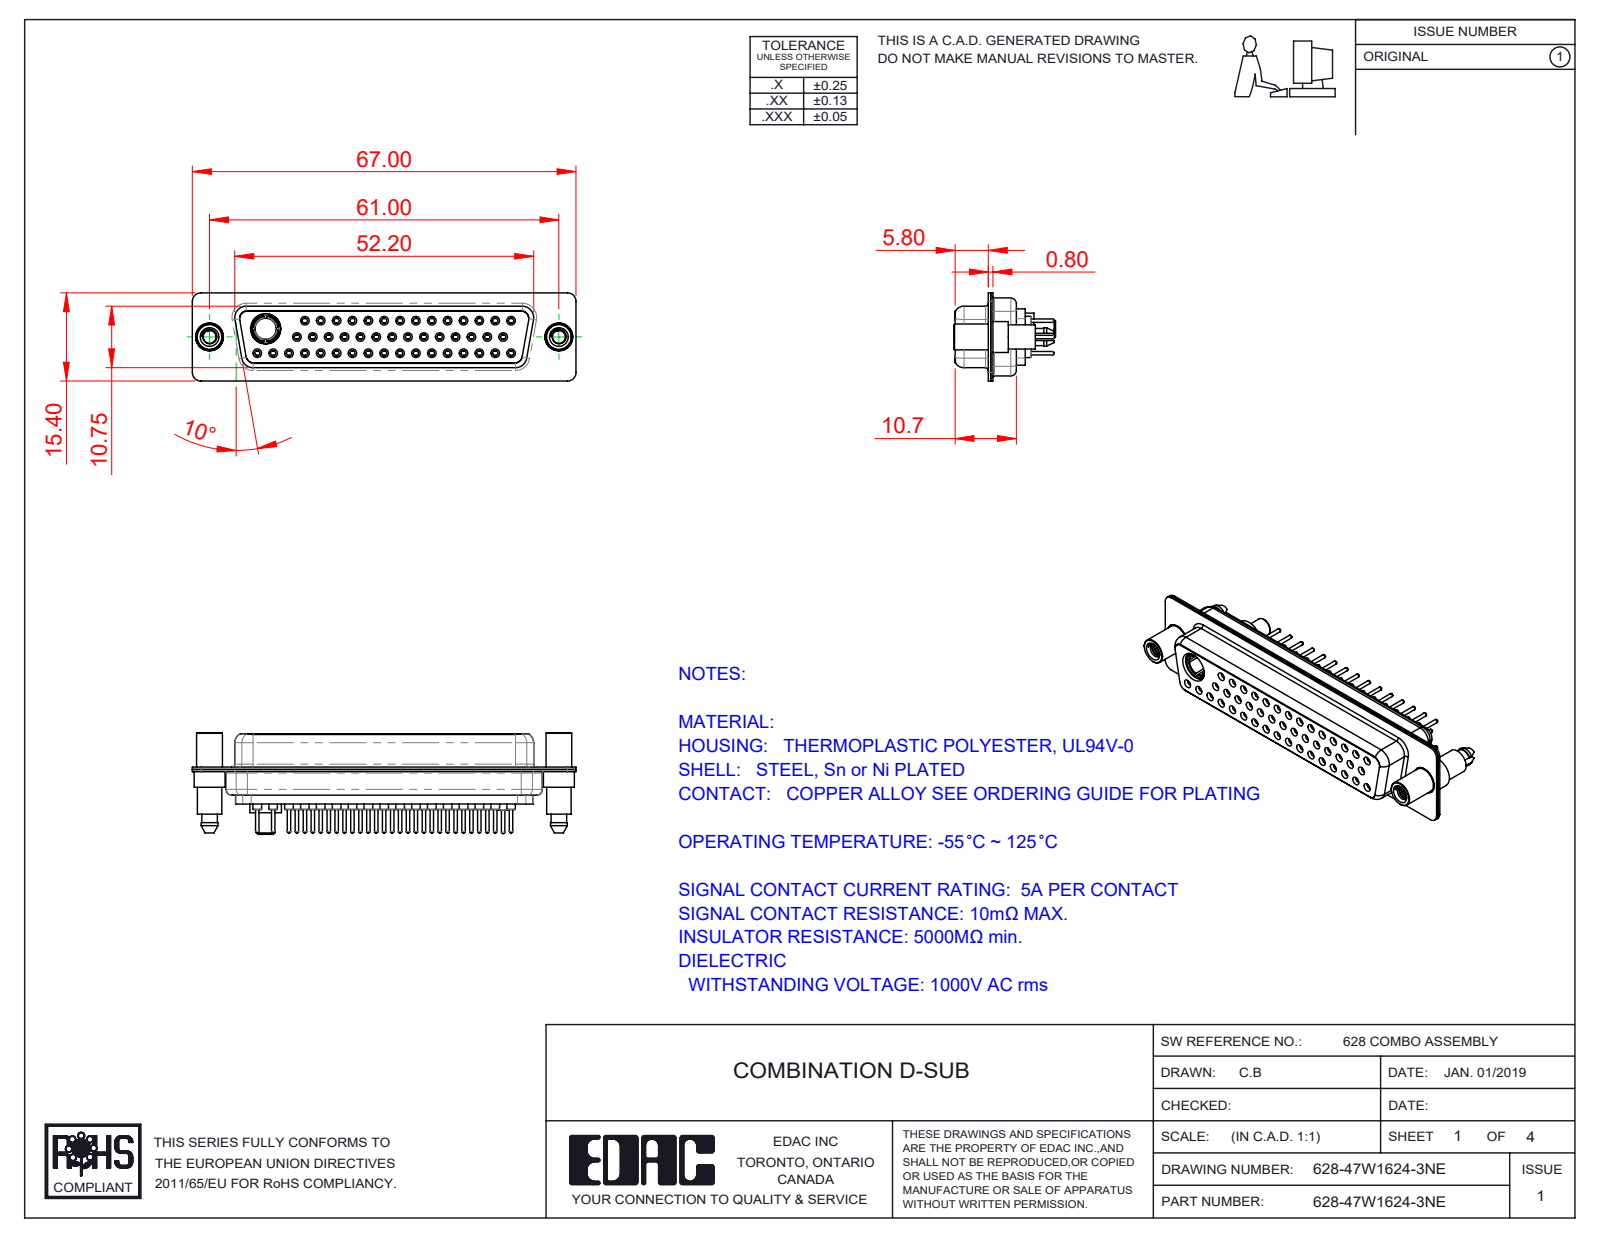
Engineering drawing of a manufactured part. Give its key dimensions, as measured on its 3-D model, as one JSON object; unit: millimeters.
{"part_name": "628Combo Contact Row 2_24; Power Socket_30A S; 628Combo Contact Row 1_24; 628Combo Threaded Standoff and Boardlock_E (+5 more)", "step_written_by": "SolidWorks 2016 (CONFIG_CONTROL_DESIGN)", "units": "millimeters", "bodies": {"solids": 53, "faces": 2929, "planar": 801, "cylindrical": 1062, "other": 1066}, "overall_size": [67, 17.75, 15.4], "volume_mm3": 7435, "surface_area_mm2": 15158, "round_holes": [[1.1, 46], [0.9, 45], [1.5, 45], [2, 45], [1.6, 31], [1.7, 14], [4.85, 3], [2.26, 2], [4, 2], [4.05, 2], [3.7, 1], [5.3, 1]], "round_bosses_or_shafts": [[2.2, 46], [0.6, 46], [1.6, 15], [5.4, 2], [4.95, 2], [4.8, 2], [4.5, 2], [4.25, 2]], "partial_cylinders_radius": [[1.5, 18], [1.35, 12], [2, 12], [1.6, 10], [0.25, 4], [0.5, 4], [0.6, 4], [0.65, 4]], "face_to_face_distances": [0.4, 11.33, 6.45, 6.05, 1.87, 12.25, 6.2, 5.8, 10.35, 10.93], "hole_center_spacings": [3.16, 2.77, 5.54, 8.31, 11.08, 13.85, 16.62, 19.39]}
